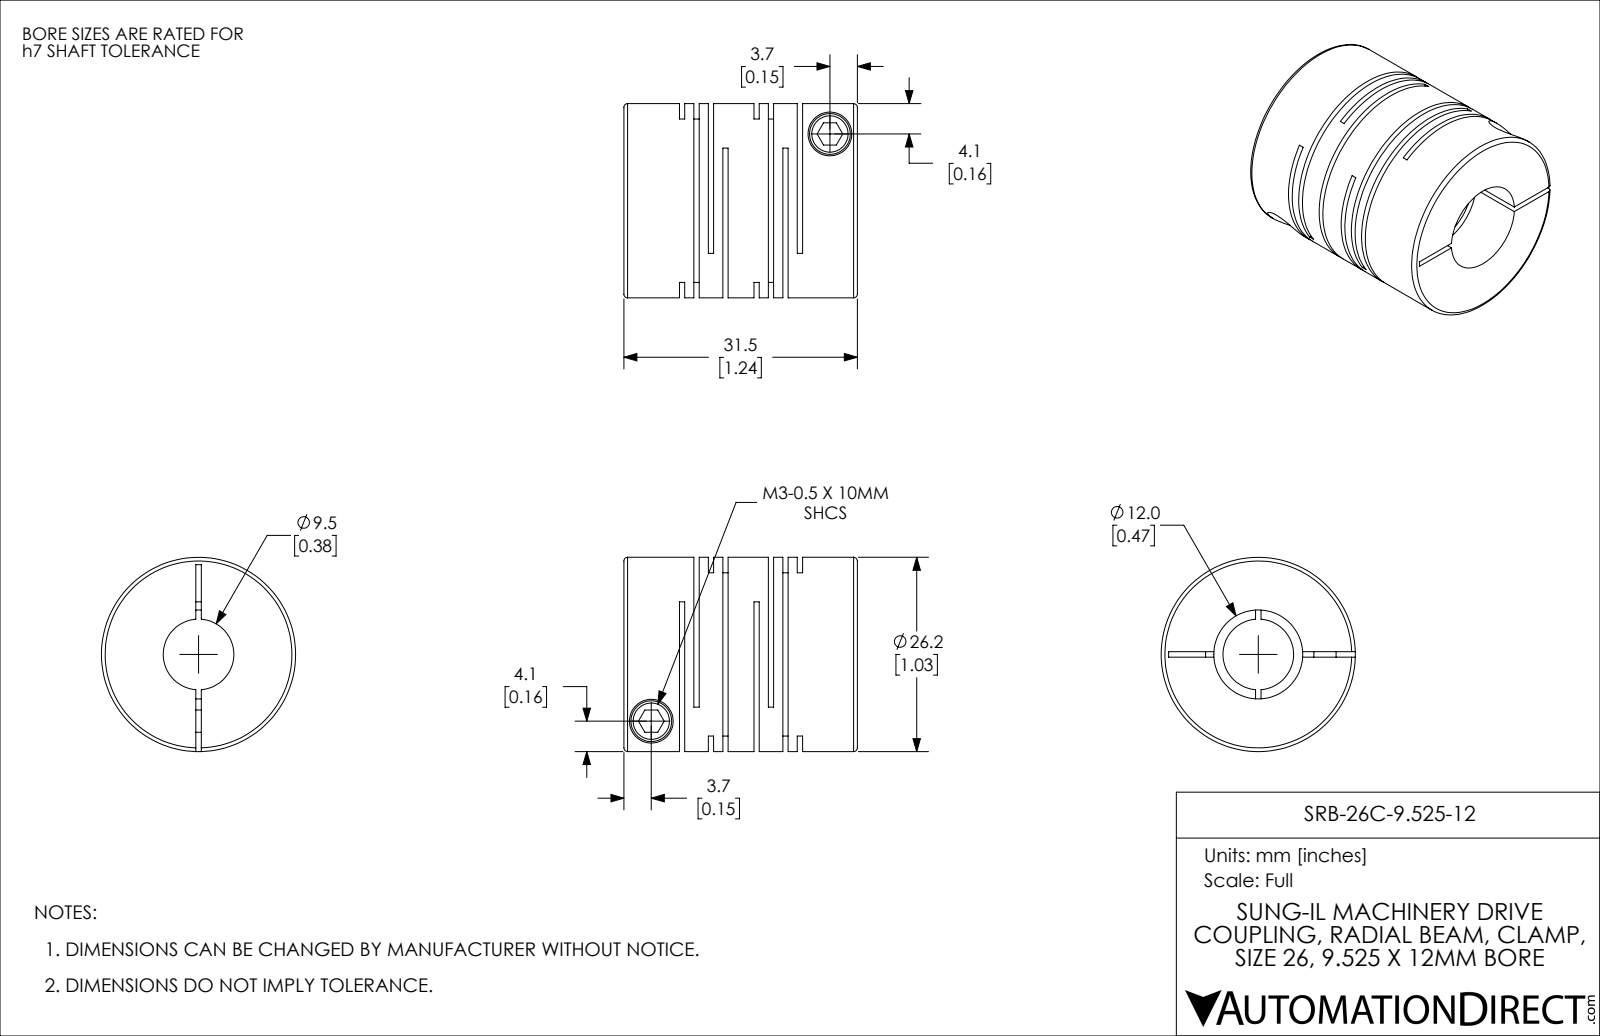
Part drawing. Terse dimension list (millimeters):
name: SRB-26C-9.525-12
written by: SolidWorks 2021 (CONFIG_CONTROL_DESIGN)
unit: mm
bodies: 1 solid, 114 faces (60 planar, 42 cylindrical, 12 other)
size: 31.5 × 26.2 × 26.2
volume: 11 373 mm³; area: 10 271 mm²
holes: 2× ⌀3, 2× ⌀5.9, 1× ⌀9.53, 1× ⌀12
bosses: 2× ⌀5.5, 1× ⌀26.2
face distances: 1.95, 10.05, 0.71, 3.9, 8.1, 12, 1.24, 2.66, 9.34, 13.95
